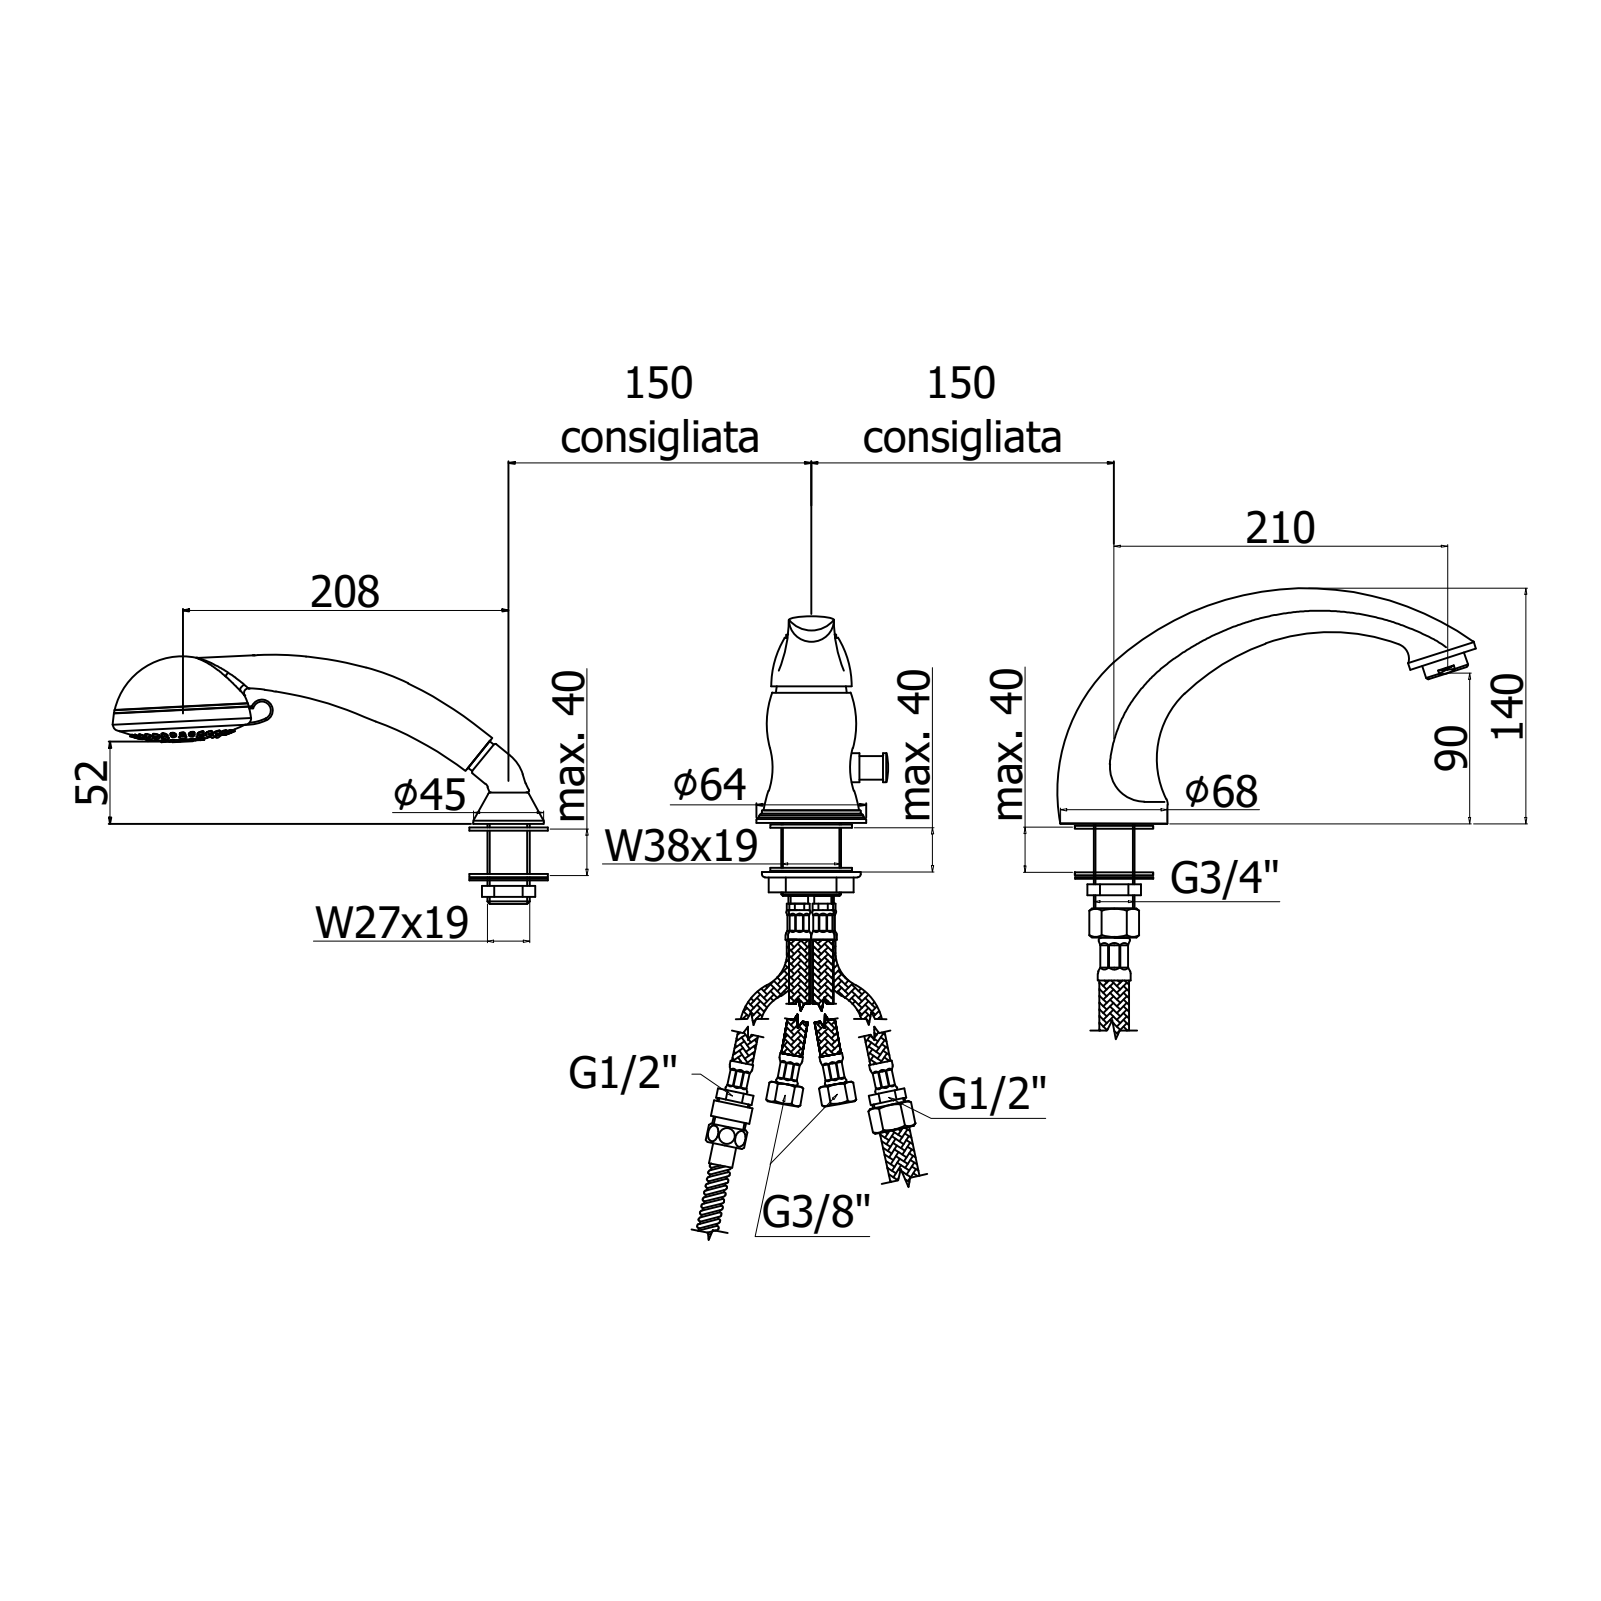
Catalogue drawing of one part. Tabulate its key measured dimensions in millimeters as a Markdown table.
| quantity | value |
| --- | --- |
| part name | FA045CR |
| STEP written by | CREO PARAMETRIC BY PTC INC, 2020044 (CONFIG_CONTROL_DESIGN) |
| units | millimeters |
| bodies | 6 solids, 5694 faces (3053 planar, 1139 cylindrical, 1502 other) |
| overall size | 371.16 × 280.95 × 150.84 |
| volume | 578 989 mm³ |
| surface area | 301 904 mm² |
| round holes (diameter × count) | 1.5 × 40, 2.5 × 16, 1.2 × 12, 3.9 × 12, 7.4 × 12, 7 × 9, 4.4 × 6, 7.2 × 4, 13.5 × 3, 3.3 × 2, 4 × 2, 6.8 × 2 |
| round bosses / shafts (diameter × count) | 4.4 × 13, 2 × 12, 6.2 × 3, 33 × 2, 22 × 2, 15 × 2, 12 × 2, 4 × 2 |
| partial cylindrical surfaces (radius × count) | 0.5 × 54, 0.3 × 33, 0.2 × 24, 1.5 × 20, 1 × 12, 3.5 × 12, 1.6 × 8, 2.2 × 8 |
| main face-to-face distances | 2.5, 6, 1.5, 1, 2.2, 3.01, 2, 10.4, 5, 4.6 |
| hole center spacings | 10.7, 15, 10.61, 18.43, 16, 37.25, 4.3, 15.01 |
